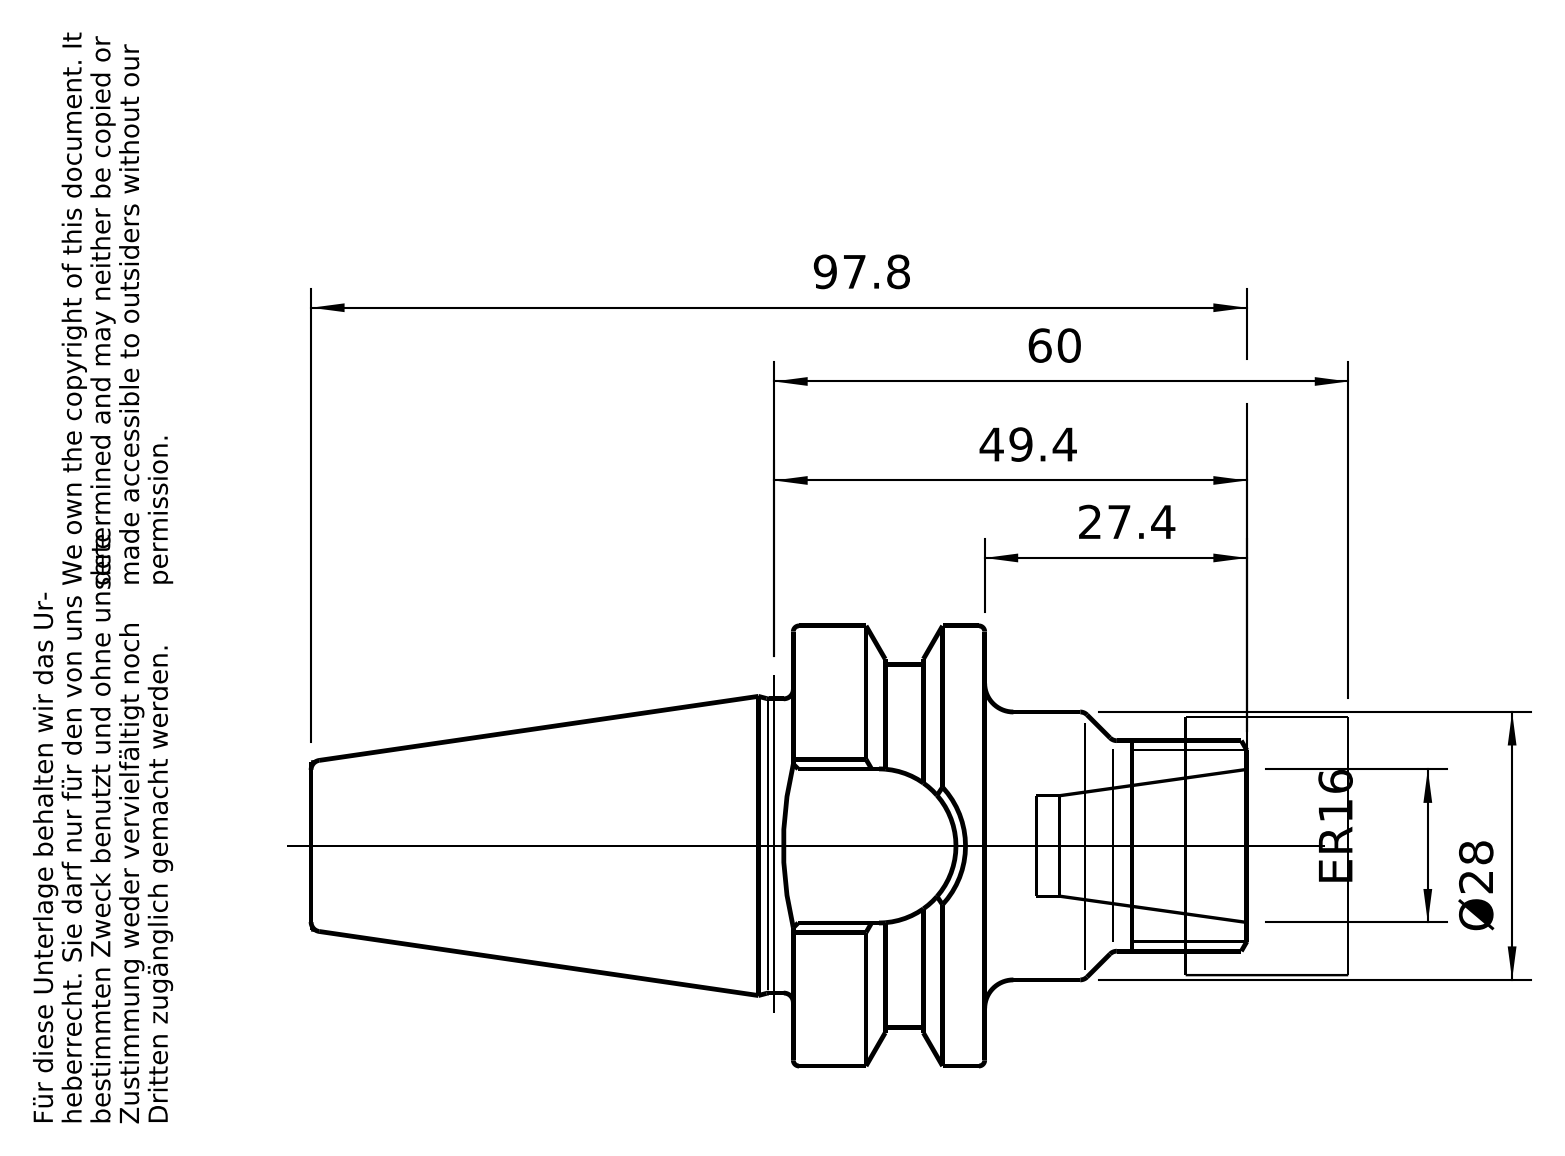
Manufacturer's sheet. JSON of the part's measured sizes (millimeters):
{"part_name": "30-520-16; 83-912-16; 30-520-16_ASM", "step_written_by": "PRO/ENGINEER BY PARAMETRIC TECHNOLOGY CORPORATION, 2010430 (CONFIG_CONTROL_DESIGN)", "units": "millimeters", "bodies": {"solids": 2, "faces": 128, "planar": 34, "cylindrical": 26, "other": 68}, "overall_size": [108.4, 45.98, 45.98], "volume_mm3": 69863, "surface_area_mm2": 17076, "round_holes": [[10.11, 1], [10.5, 1], [12.51, 1], [13, 1]], "round_bosses_or_shafts": [[45.98, 1], [30.75, 1], [28, 1], [22, 1], [12.01, 1]], "partial_cylinders_radius": [[8.1, 1], [18.88, 1]], "face_to_face_distances": [20.2, 20, 40.2, 25, 58, 38, 17.8, 32.3, 3.65, 28.65]}
